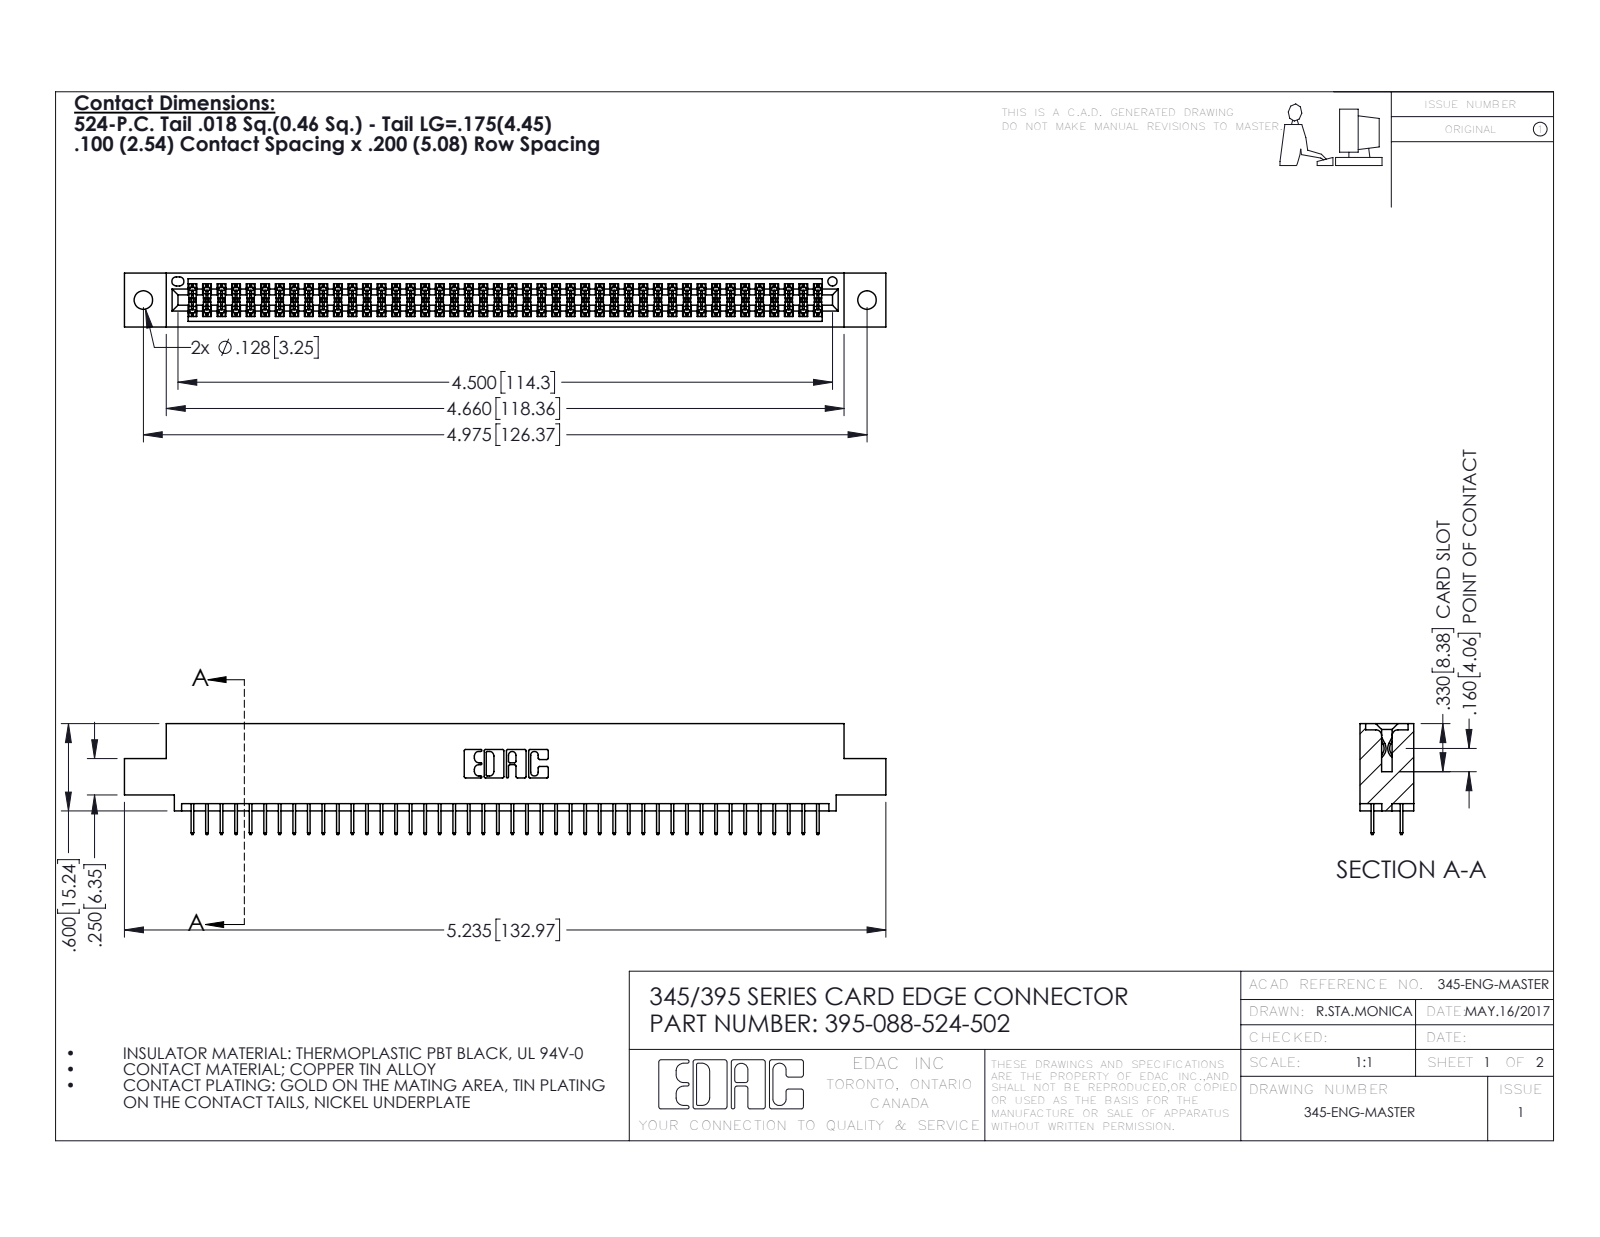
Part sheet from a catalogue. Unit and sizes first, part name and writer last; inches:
Units: inches
Overall size (bounding box): 5.235 × 0.762 × 0.37
Round holes (diameter × count): ⌀0.128 ×2, ⌀0.064 ×1
Partial cylindrical surfaces — rounded edges, fillets, slot ends (radius × count): R0.006 ×132, R0.01 ×22, R0.007 ×6, R0.031 ×6, R0.026 ×3, R0.014 ×2, R0.019 ×2, R0.022 ×2
Main face-to-face distances: 0.072, 0.298, 0.2, 0.37, 0.098, 0.272, 0.025, 0.225, 0.072, 0.175
Hole centre spacings: 0.27, 4.739, 4.975
Volume: 0.775 in³ · Surface area: 28.32 in²
Bodies: 89 solids, 4882 faces (3516 planar, 1366 cylindrical, 0 other)
Part name (STEP PRODUCT): 345 Part_0.110 Offset - 0.128 Dia; 395-088-524-502; 345-292-001_345-293-124
STEP written by: SolidWorks 2016 (CONFIG_CONTROL_DESIGN)
